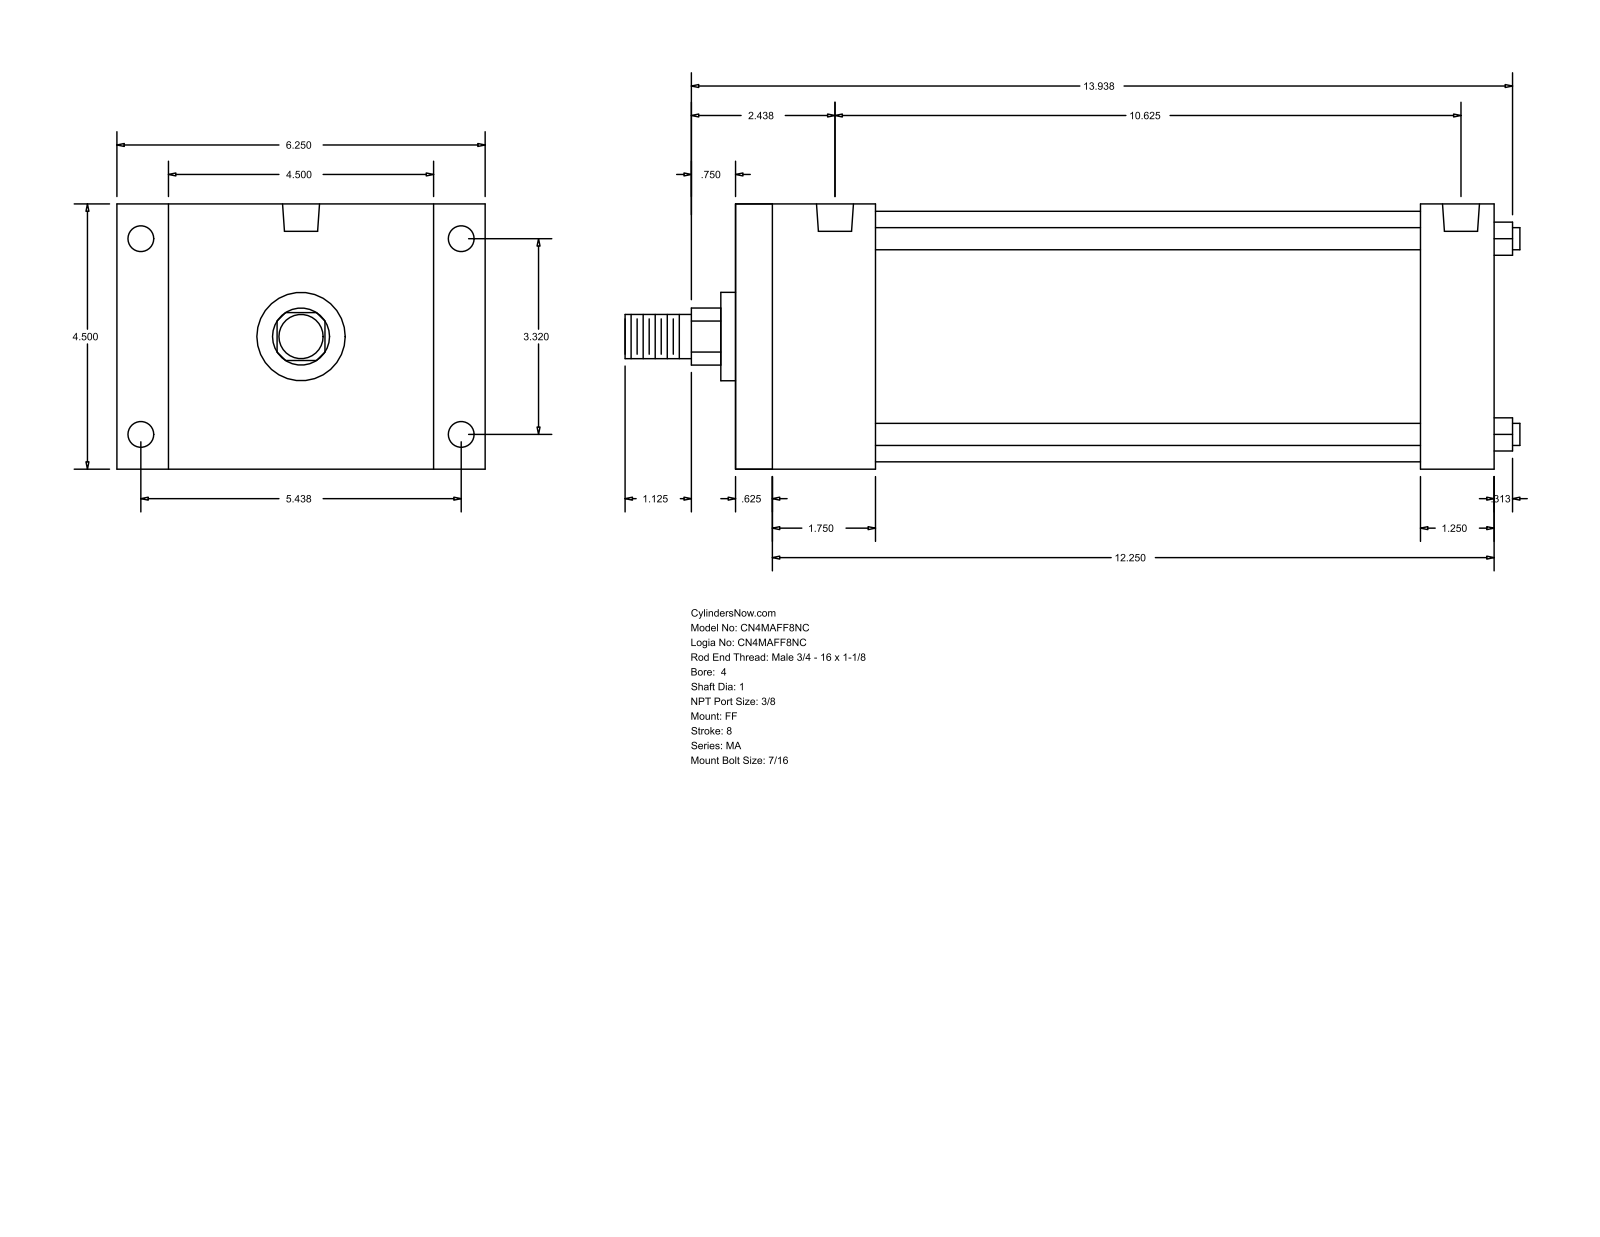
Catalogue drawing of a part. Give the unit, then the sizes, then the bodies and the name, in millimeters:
Units: millimetres
Overall size (bounding box): 385.76 × 158.75 × 114.3
Round holes (diameter × count): ⌀11.11 ×8, ⌀15.93 ×2
Round bosses / shafts (diameter × count): ⌀9.53 ×4, ⌀107.95 ×1, ⌀38.1 ×1, ⌀25.4 ×1, ⌀19.05 ×1
Partial cylindrical surfaces — rounded edges, fillets, slot ends (radius × count): R12.29 ×1
Main face-to-face distances: 114.3, 327.02, 15.87, 311.15, 22.23, 136.53, 295.27, 279.4, 31.75, 60.33
Hole centre spacings: 84.32, 138.12, 161.82, 260.35, 4.76, 4.77, 265.11, 265.12
Bodies: 0 solids, 92 faces (64 planar, 28 cylindrical, 0 other)
Part name (STEP PRODUCT): MA_FF__0400_1
STEP written by: GSSL Pune (CONFIG_CONTROL_DESIGN)
